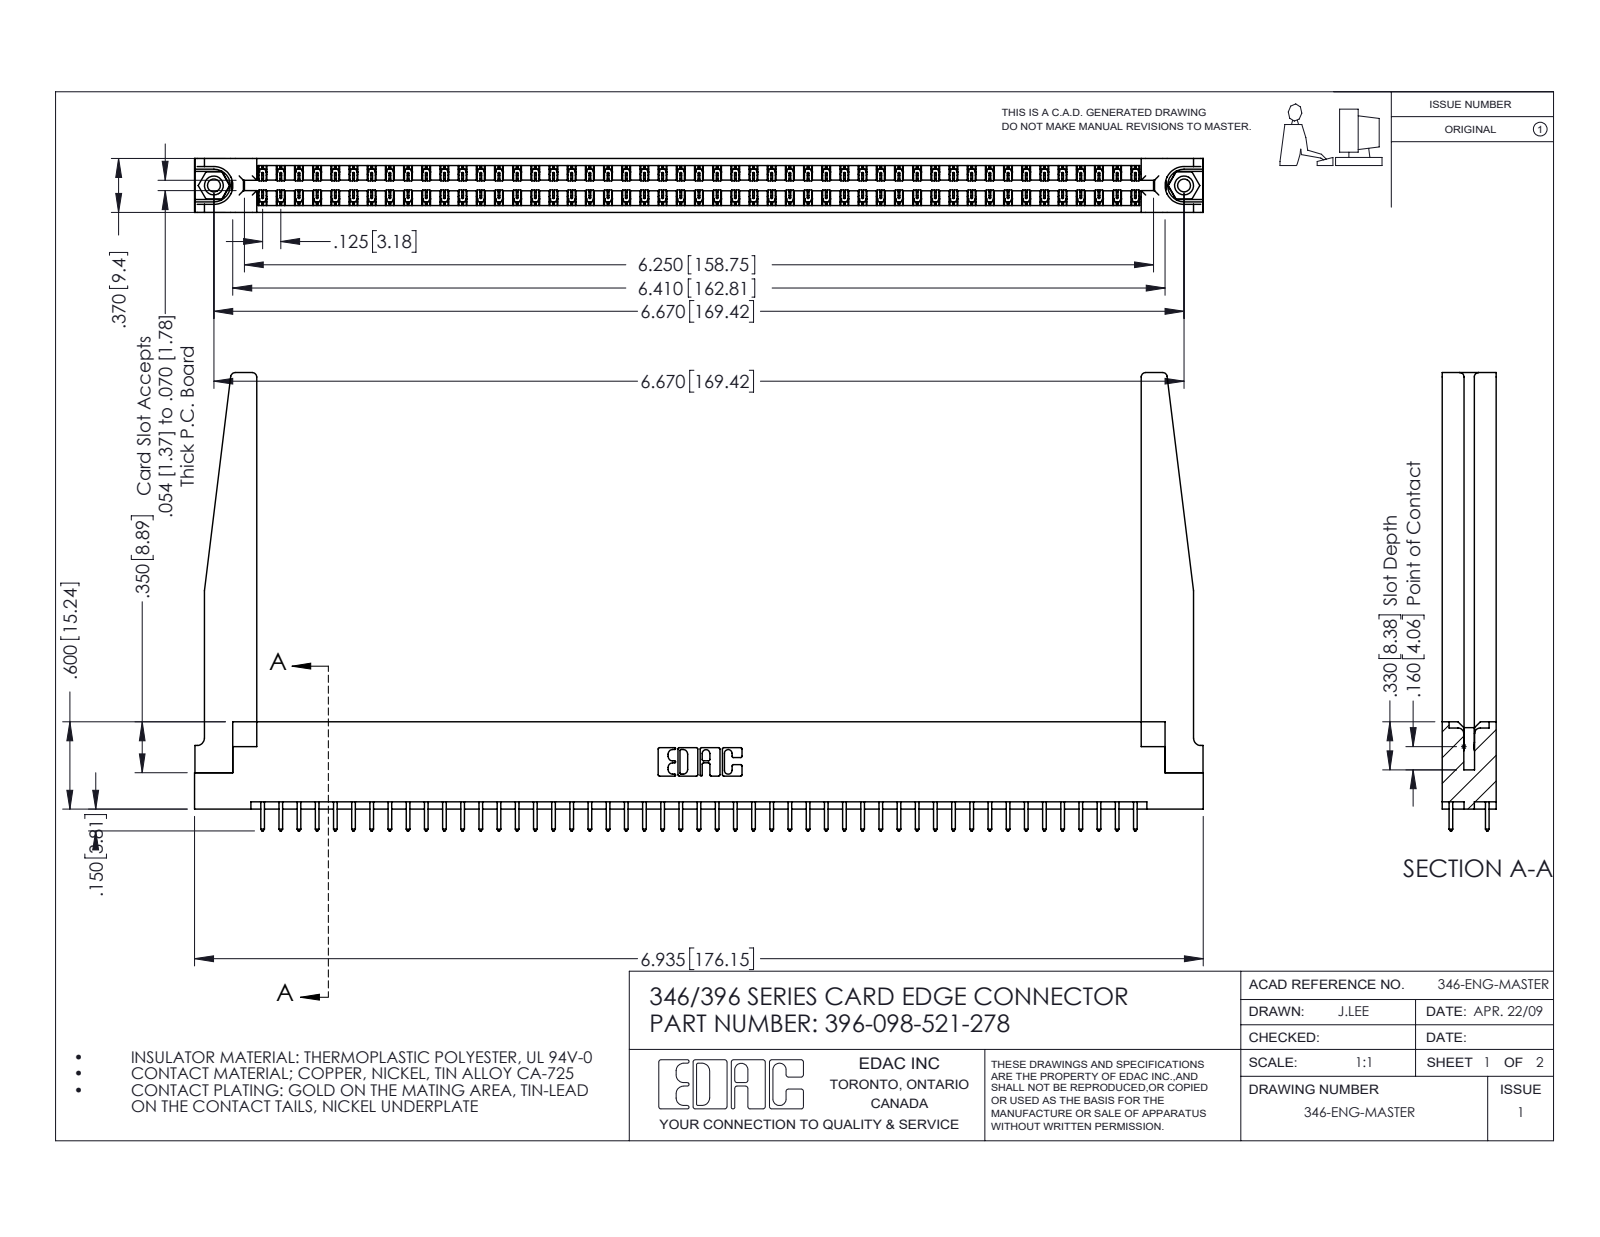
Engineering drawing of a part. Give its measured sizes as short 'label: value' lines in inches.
name: 396-098-521-278; 346 Part_Flush Mounting Lugs - 0.156 Dia-TH; 345-292-001_345-293-121; 346-220-078_345-220-078 (+1 more)
written by: SolidWorks 2016 (CONFIG_CONTROL_DESIGN)
unit: in
bodies: 103 solids, 5452 faces (3648 planar, 1752 cylindrical, 52 other)
size: 6.935 × 3.15 × 0.37
volume: 1.471 in³; area: 46.51 in²
holes: 2× ⌀0.089, 2× ⌀0.125, 2× ⌀0.156, 1× ⌀0.064
bosses: 2× ⌀0.155
rounds: 147× R0.006, 98× R0.01, 22× R0.01, 8× R0.03, 6× R0.007, 6× R0.031, 3× R0.026, 2× R0.014
face distances: 0.37, 0.048, 0.322, 0.072, 0.25, 0.15, 0.148, 0.298, 0.025, 0.275
hole spacings: 0.246, 6.461, 6.67
